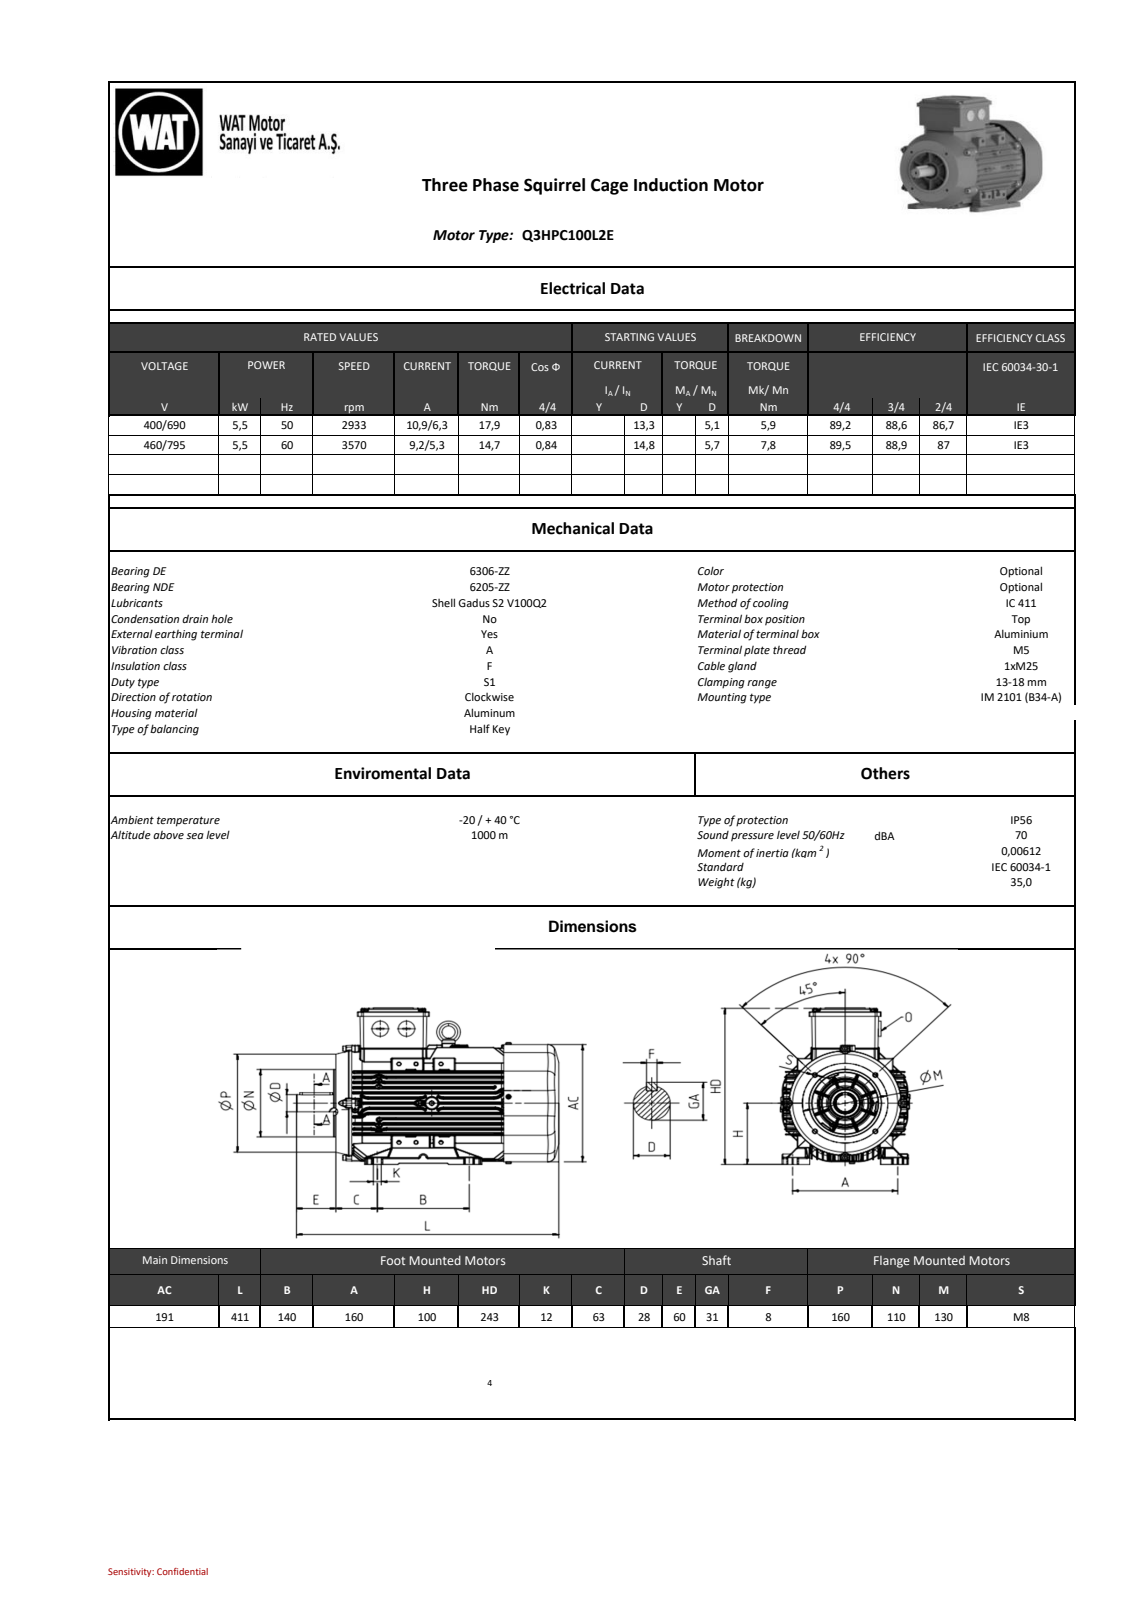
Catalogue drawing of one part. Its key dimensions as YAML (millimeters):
part_name: "QH100 B35 KTA-M2_stp_objects"
step_written_by: "SIEMENS PLM Software NX2206.8101 (AUTOMOTIVE_DESIGN)"
units: millimeters
bodies: {solids: 0, faces: 5581, planar: 1205, cylindrical: 2126, other: 2250}
overall_size: [411.25, 242.57, 197.57]
round_holes:
  - {diameter: 6.5, count: 4}
  - {diameter: 6.8, count: 4}
  - {diameter: 10, count: 1}
  - {diameter: 10.5, count: 1}
  - {diameter: 12, count: 1}
  - {diameter: 43.9, count: 1}
  - {diameter: 44.1, count: 1}
  - {diameter: 52, count: 1}
  - {diameter: 57.4, count: 1}
  - {diameter: 89, count: 1}
  - {diameter: 129, count: 1}
round_bosses_or_shafts:
  - {diameter: 8, count: 8}
  - {diameter: 12, count: 4}
  - {diameter: 113.5, count: 1}
  - {diameter: 110, count: 1}
  - {diameter: 93.5, count: 1}
  - {diameter: 61, count: 1}
  - {diameter: 30, count: 1}
  - {diameter: 29, count: 1}
partial_cylinders:
  - {radius: 0.8, count: 565}
  - {radius: 1, count: 487}
  - {radius: 2, count: 116}
  - {radius: 1.5, count: 80}
  - {radius: 0.81, count: 51}
  - {radius: 0.5, count: 36}
  - {radius: 5, count: 36}
  - {radius: 15, count: 26}
face_to_face_distances: [8.53, 8.46, 8.45, 76.24, 16.91, 93.45, 25.58, 17.05, 76.68, 59.63]
hole_center_spacings: [65, 91.92, 64, 66.95, 105.32, 128, 129.99, 143.11]
